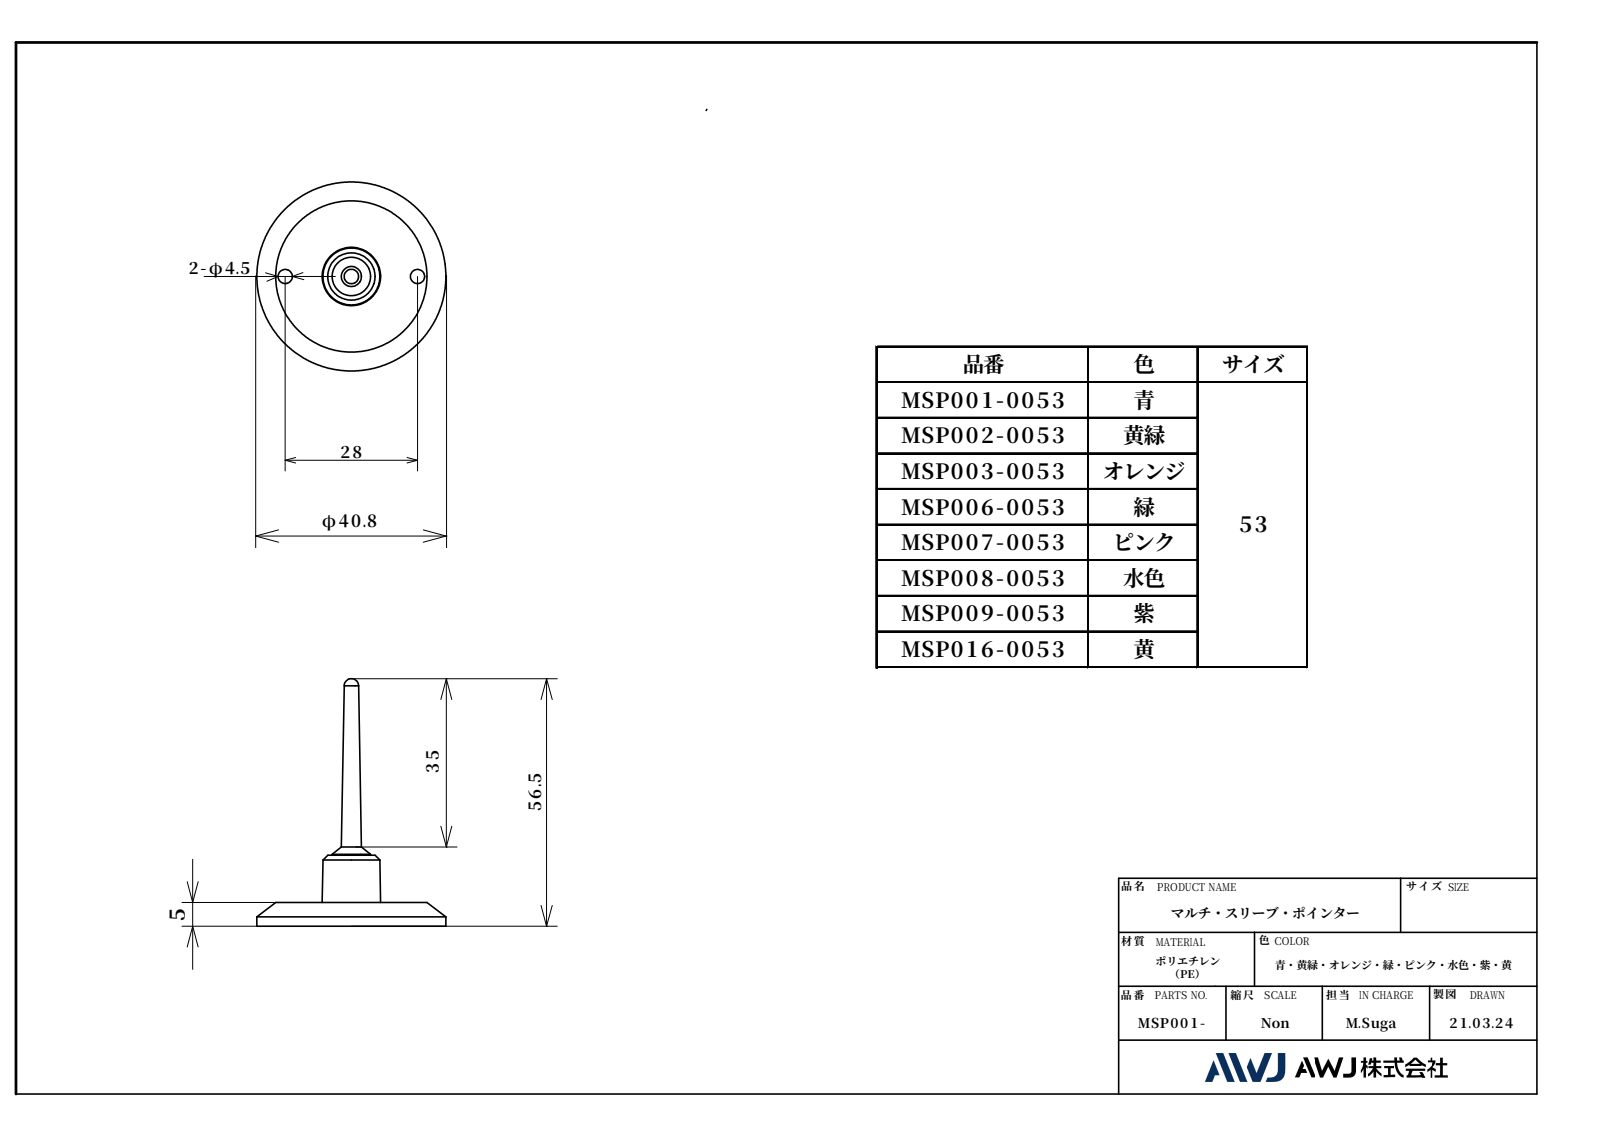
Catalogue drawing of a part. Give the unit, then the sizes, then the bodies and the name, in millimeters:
Units: millimetres
Overall size (bounding box): 56.5 × 40.87 × 40.87
Round holes (diameter × count): ⌀4.5 ×2, ⌀2.9 ×1, ⌀4 ×1, ⌀6 ×1, ⌀8 ×1
Partial cylindrical surfaces — rounded edges, fillets, slot ends (radius × count): R0.1 ×4, R0.89 ×1, R1.33 ×1
Main face-to-face distances: 5, 3, 2, 1.5, 3.5, 15, 16.5, 5.2, 3.7, 2.2
Hole centre spacings: 14, 28
Volume: 6 861 mm³ · Surface area: 5 817 mm²
Bodies: 2 solids, 118 faces (75 planar, 14 cylindrical, 29 other)
STEP written by: XStep 1.0 (CONFIG_CONTROL_DESIGN)
